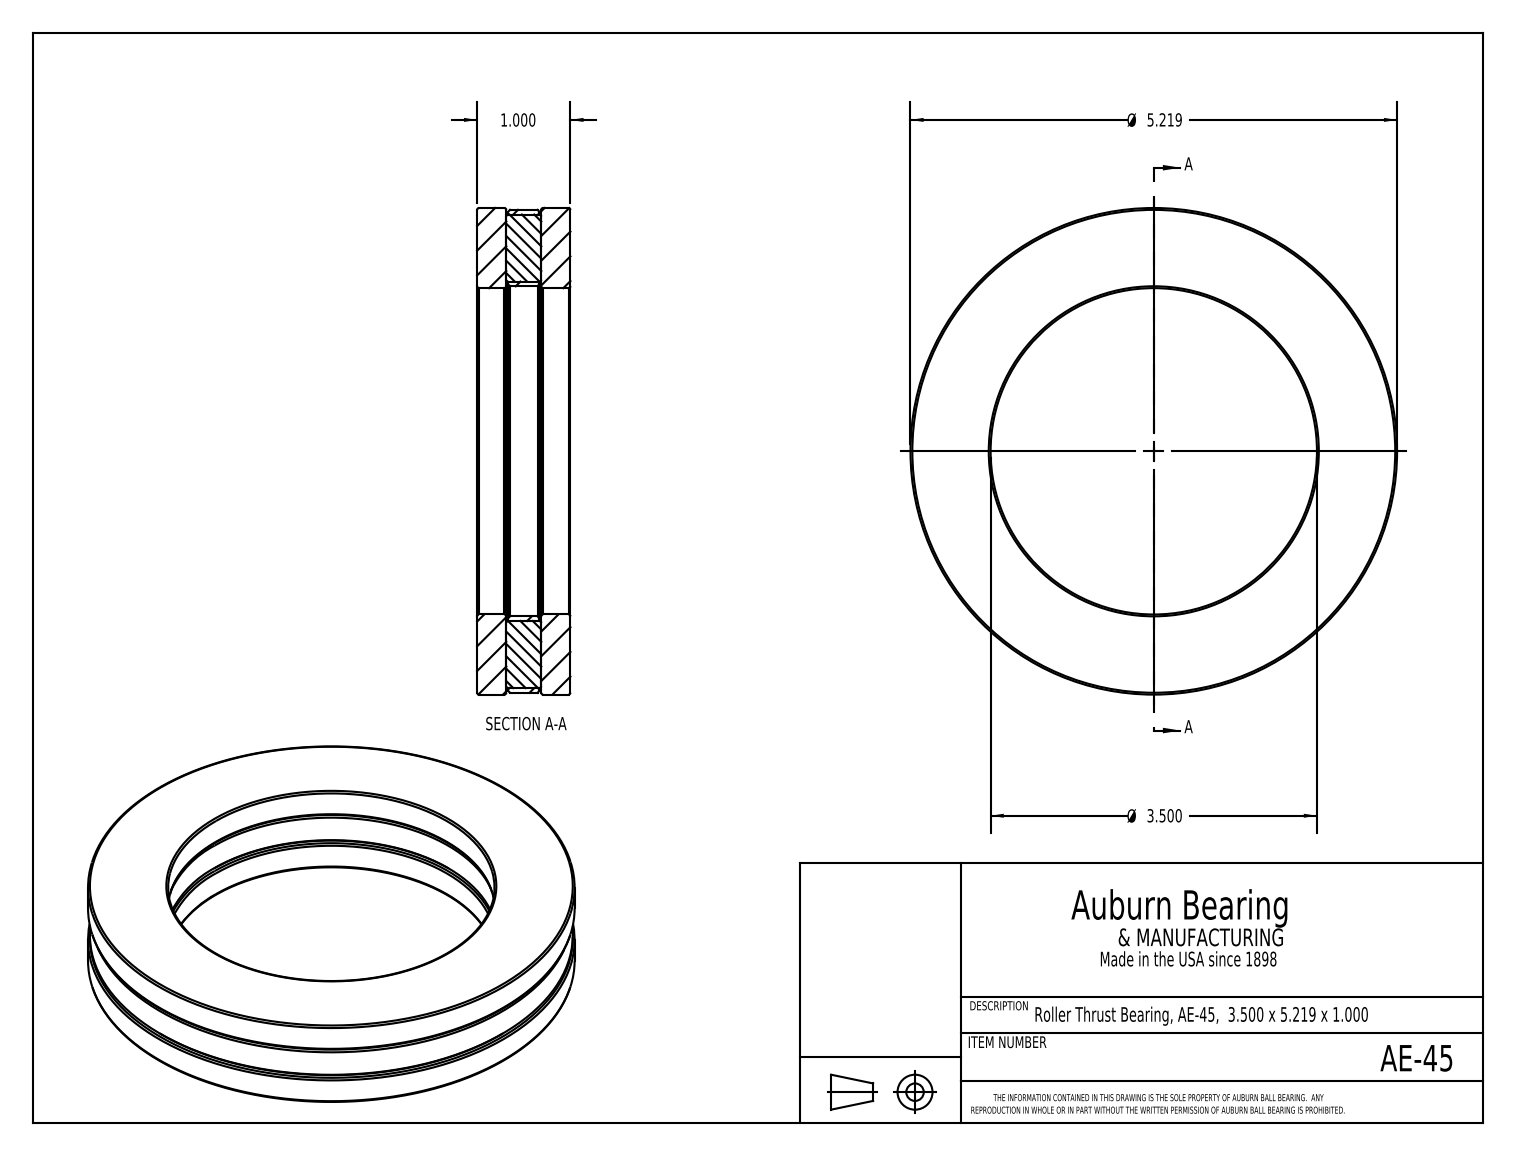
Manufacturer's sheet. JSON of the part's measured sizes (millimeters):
{"part_name": "AE-45", "step_written_by": "SolidWorks 2017 (CONFIG_CONTROL_DESIGN)", "units": "millimeters", "bodies": {"solids": 7, "faces": 60, "planar": 30, "cylindrical": 10, "other": 20}, "overall_size": [132.6, 132.6, 25.4], "volume_mm3": 181100, "surface_area_mm2": 64000, "round_holes": [[88.9, 1], [89.9, 1]], "round_bosses_or_shafts": [[9.5, 2], [132.6, 1], [131.5, 1]], "face_to_face_distances": [8, 17.4, 8.5, 16.9, 0.5, 9, 9.5, 25.4, 8.5, 41.5]}
